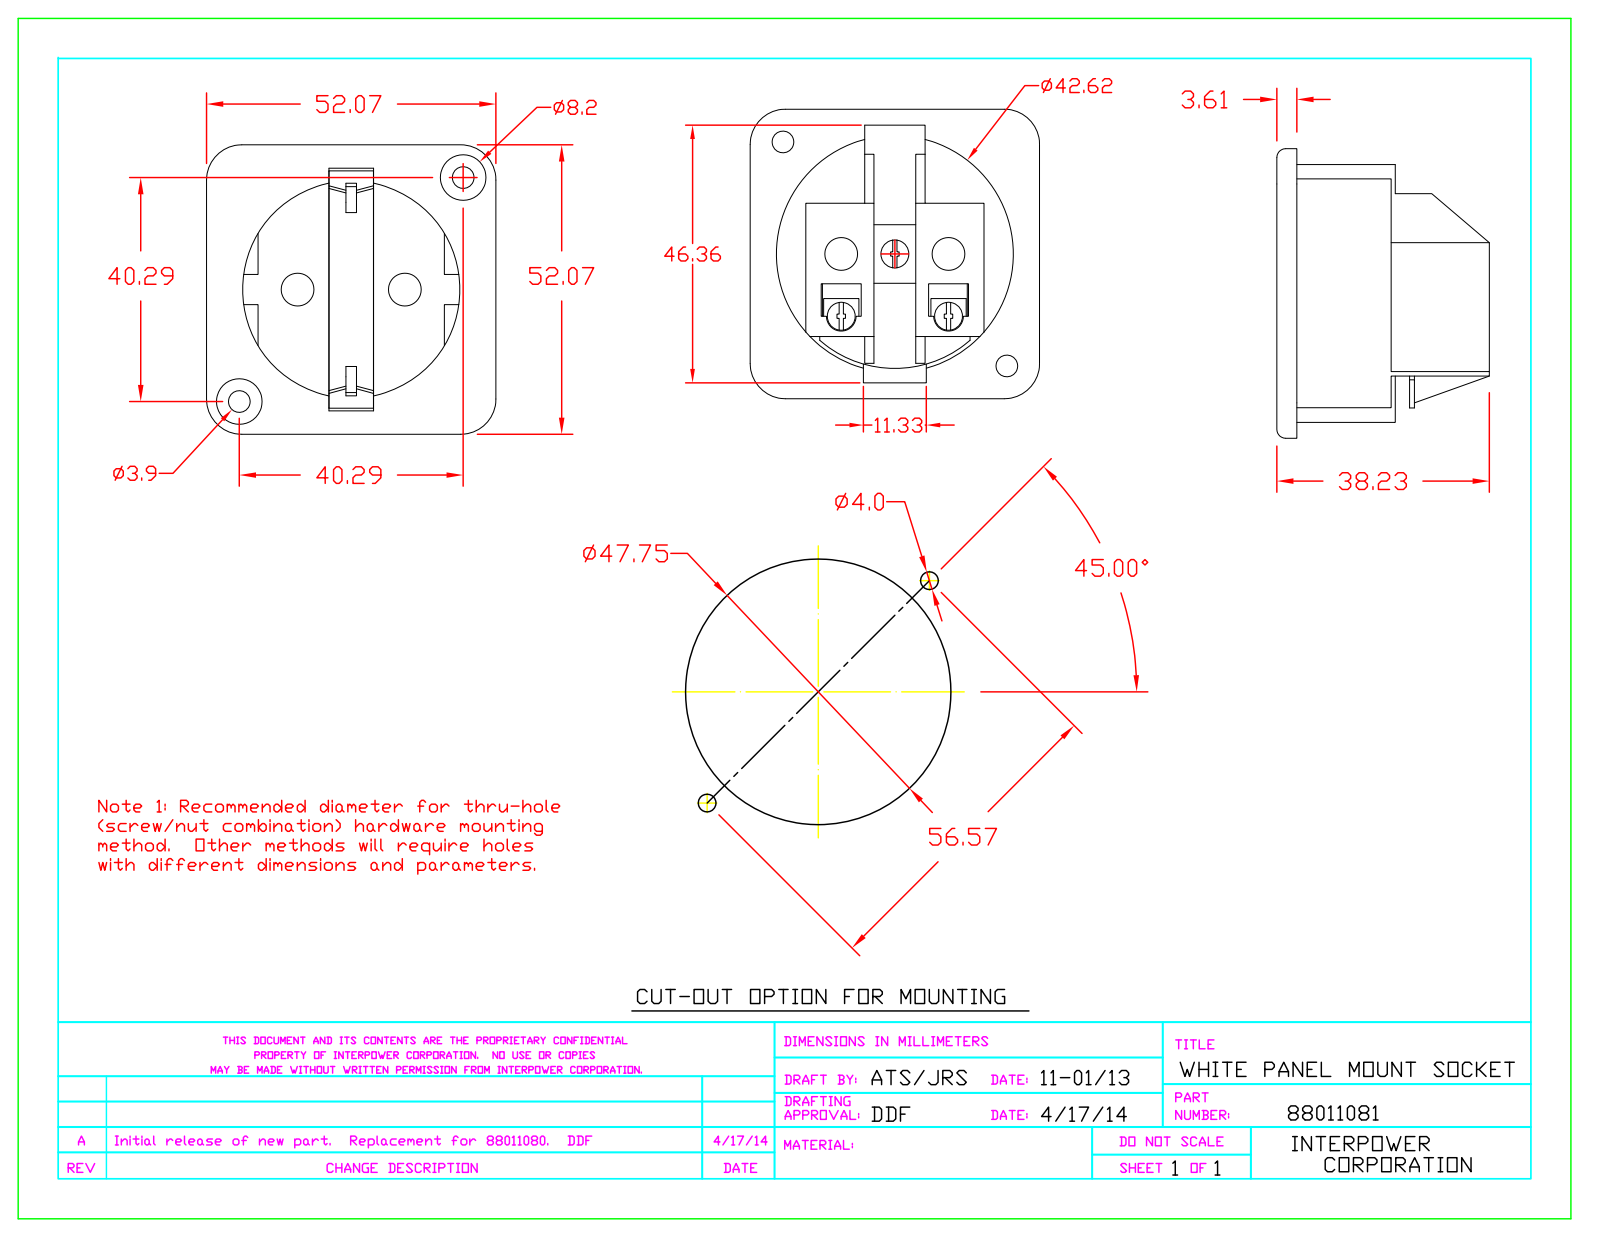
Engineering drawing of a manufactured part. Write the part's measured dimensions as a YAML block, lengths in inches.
part_name: "88011081"
step_written_by: "SolidWorks 2013 (CONFIG_CONTROL_DESIGN)"
units: inches
bodies: {solids: 1, faces: 230, planar: 169, cylindrical: 53, other: 8}
overall_size: [2.05, 2.05, 1.505]
volume: 1.168
surface_area: 28.47
round_holes:
  - {diameter: 0.154, count: 2}
  - {diameter: 0.232, count: 2}
  - {diameter: 1.54, count: 1}
round_bosses_or_shafts:
  - {diameter: 0.198, count: 3}
  - {diameter: 0.1, count: 3}
  - {diameter: 1.678, count: 1}
partial_cylinders:
  - {radius: 0.062, count: 4}
  - {radius: 0.25, count: 4}
  - {radius: 0.04, count: 2}
  - {radius: 0.05, count: 2}
  - {radius: 0.06, count: 2}
  - {radius: 0.1, count: 2}
  - {radius: 0.105, count: 2}
  - {radius: 0.811, count: 1}
face_to_face_distances: [0.365, 0.142, 0.575, 0.668, 0.296, 0.717, 0.483, 0.779, 0.81, 0.093]
hole_center_spacings: [0.38, 0.894, 1.121, 1.416, 0.76, 2.243]
